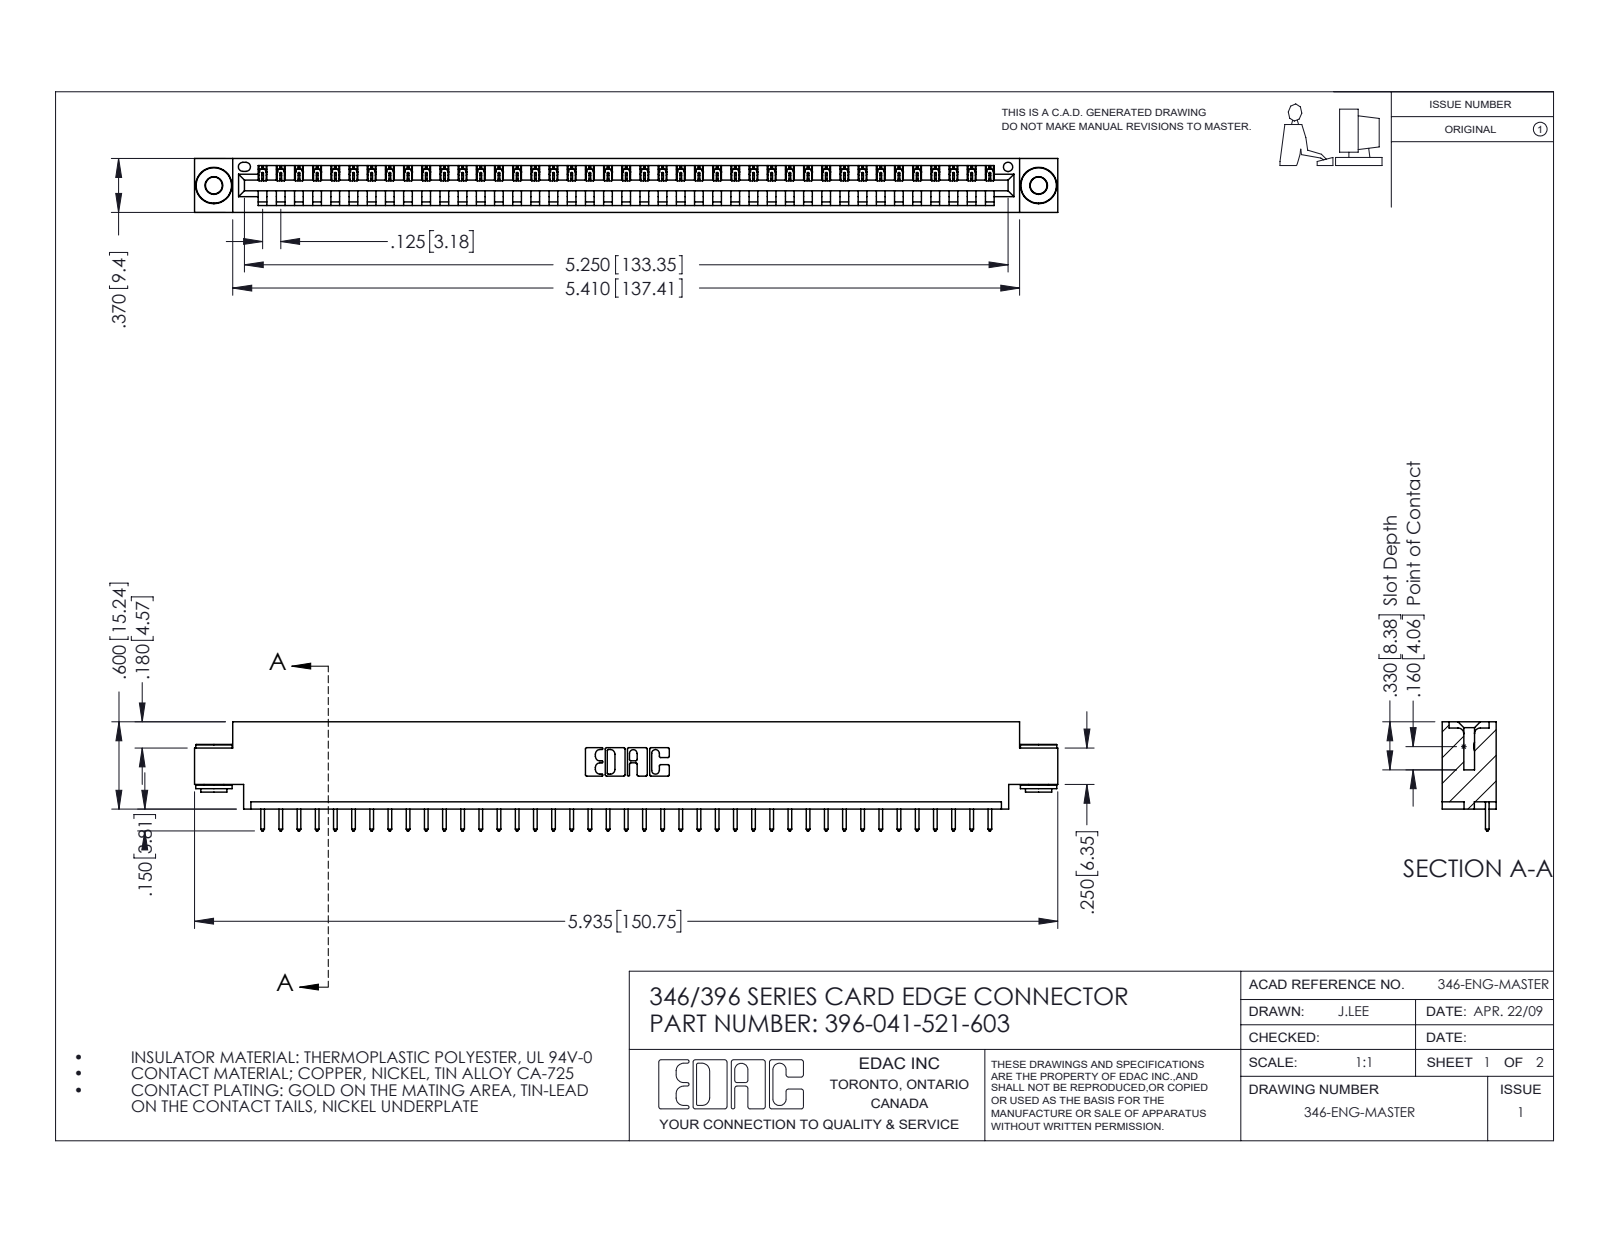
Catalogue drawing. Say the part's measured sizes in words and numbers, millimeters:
The part is named "346 Part_0.170 Offset - 0.156 Dia-TH; 345-250-002_345-250-002-102; 345-292-001_345-293-121; 396-041-521-603". Its 3-D file was written by "SolidWorks 2016 (CONFIG_CONTROL_DESIGN)". It is 44 solids with 2542 faces: 1730 planar, 804 cylindrical and 8 other. Overall it measures 150.7 by 19.1 by 9.4 millimeters. Its volume is 14 200 cubic millimeters and its surface area 17 620 square millimeters. Round holes: 2 of diameter 2.9, 2 of diameter 4, 1 of diameter 1.6. Round bosses or shafts: 2 of diameter 6.4, 2 of diameter 4.6, 2 of diameter 3.5. Partial cylindrical surfaces (rounded edges, fillets, slot ends): 82 of radius 0.2, 82 of radius 0.3, 22 of radius 0.3, 6 of radius 0.2, 6 of radius 0.8, 3 of radius 0.7, 2 of radius 0.8, 2 of radius 1. The main face-to-face distances are 1.2, 8.2, 9.4, 6.4, 0.6, 1.8, 7.6, 3.8, 5.6, 2.5. The hole center spacings are 6.2, 138.7, 144.
